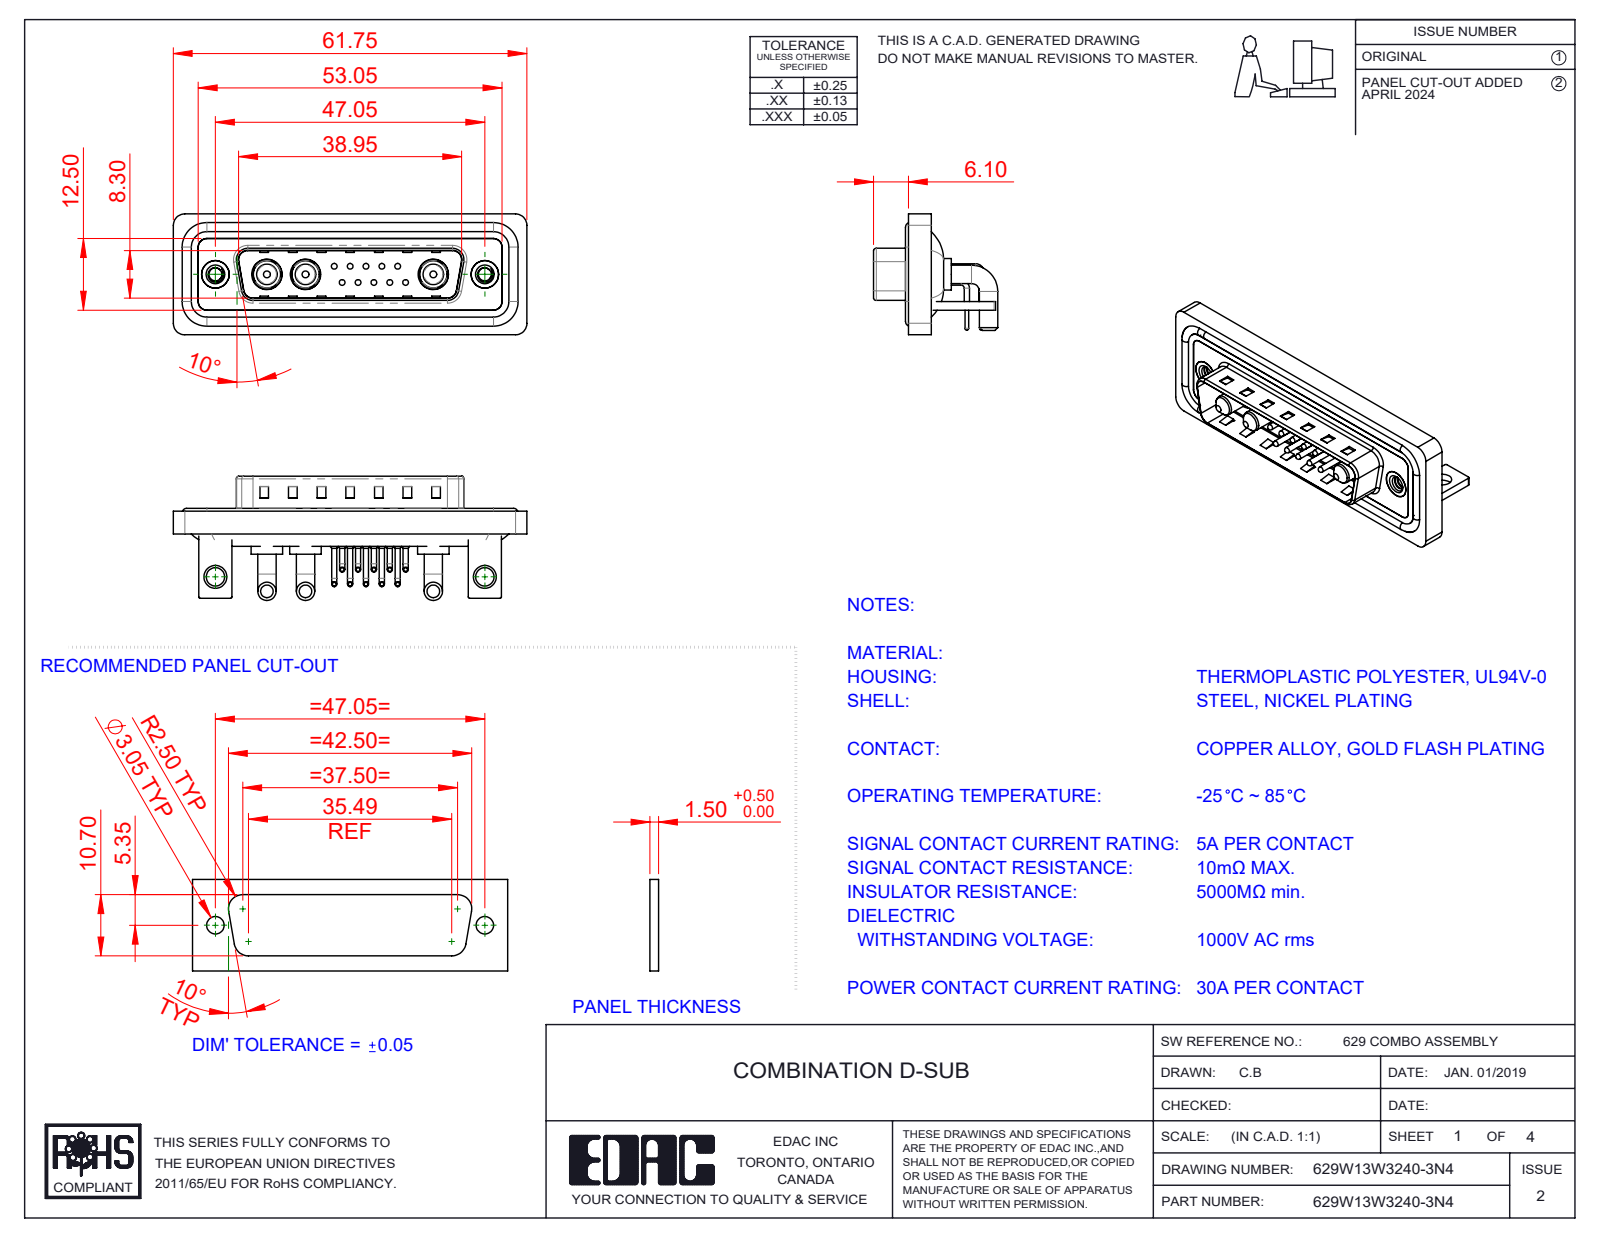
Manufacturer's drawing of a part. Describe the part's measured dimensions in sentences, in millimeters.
The part is named "629Combo Waterproof Housing_25 Contacts; 629Combo Housing_13W3; 629Combo Shell Front_25 Contacts; 629Combo Contact Row 2 (+6 more)". Its 3-D file was written by "SolidWorks 2023 (CONFIG_CONTROL_DESIGN)". It is 25 solids with 1752 faces: 899 planar, 629 cylindrical and 224 other. Overall it measures 61.75 by 21.7 by 21.1 millimeters. Its volume is 7 972 cubic millimeters and its surface area 13 138 square millimeters. Round holes: 10 of diameter 0.75, 10 of diameter 1.6, 10 of diameter 2, 3 of diameter 4.85, 3 of diameter 5.3, 2 of diameter 2.26, 2 of diameter 3.2, 2 of diameter 4, 2 of diameter 4.8, 2 of diameter 5. Round bosses or shafts: 20 of diameter 0.9, 10 of diameter 1.5, 10 of diameter 1, 10 of diameter 0.65, 6 of diameter 3.2, 4 of diameter 1.6, 3 of diameter 5.5, 3 of diameter 5.2. Partial cylindrical surfaces (rounded edges, fillets, slot ends): 19 of radius 2, 18 of radius 1.5, 16 of radius 0.25, 10 of radius 1.01, 9 of radius 0.5, 8 of radius 1.6, 4 of radius 0.6, 4 of radius 0.65. The main face-to-face distances are 0.4, 0.8, 1.5, 2.9, 2.1, 1.1, 4.1, 1.6, 3.7, 4.5. The hole center spacings are 3.16, 2.77, 5.04, 5.54, 7.49, 5.03, 8.31, 10.11.
